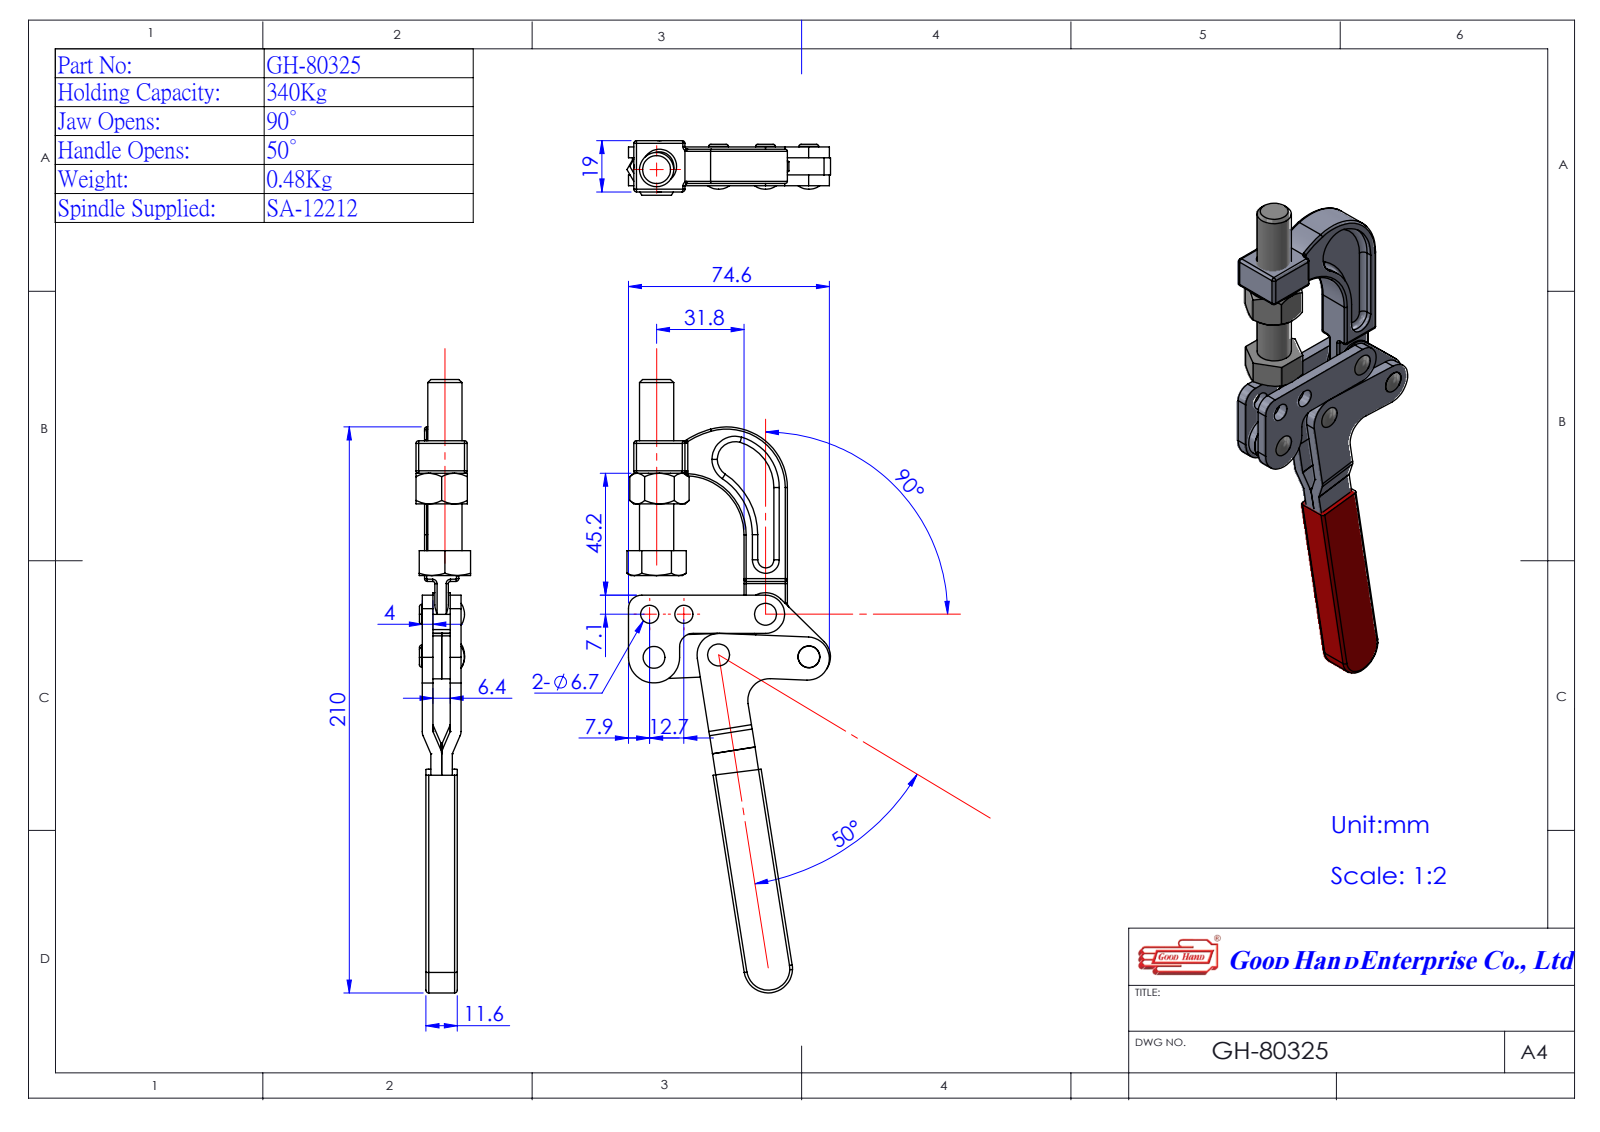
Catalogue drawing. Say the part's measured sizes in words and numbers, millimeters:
The part is named "Group3^EMC80325; Group4^EMC80325; Group1^EMC80325; Group5^EMC80325 (+1 more)". Its 3-D file was written by "SolidWorks 2016 (AUTOMOTIVE_DESIGN)". It is 3 solids with 247 faces: 114 planar, 87 cylindrical and 46 other. Overall it measures 236.1 by 75.01 by 19.05 millimeters. Its volume is 40 224 cubic millimeters and its surface area 33 046 square millimeters. Round holes: 4 of diameter 5, 2 of diameter 6.7. Round bosses or shafts: 4 of diameter 7.3, 1 of diameter 12.7. Partial cylindrical surfaces (rounded edges, fillets, slot ends): 6 of radius 8, 4 of radius 0.1, 4 of radius 4.1, 2 of radius 1, 2 of radius 5, 1 of radius 2, 1 of radius 4.95, 1 of radius 7.1. The main face-to-face distances are 4, 10.4, 6.4, 13, 1.4, 2.6, 9, 4.8, 14.4, 0.8. The hole center spacings are 12.7, 16.08, 19.47, 19.85, 22.42, 23.05, 24, 29.7.
